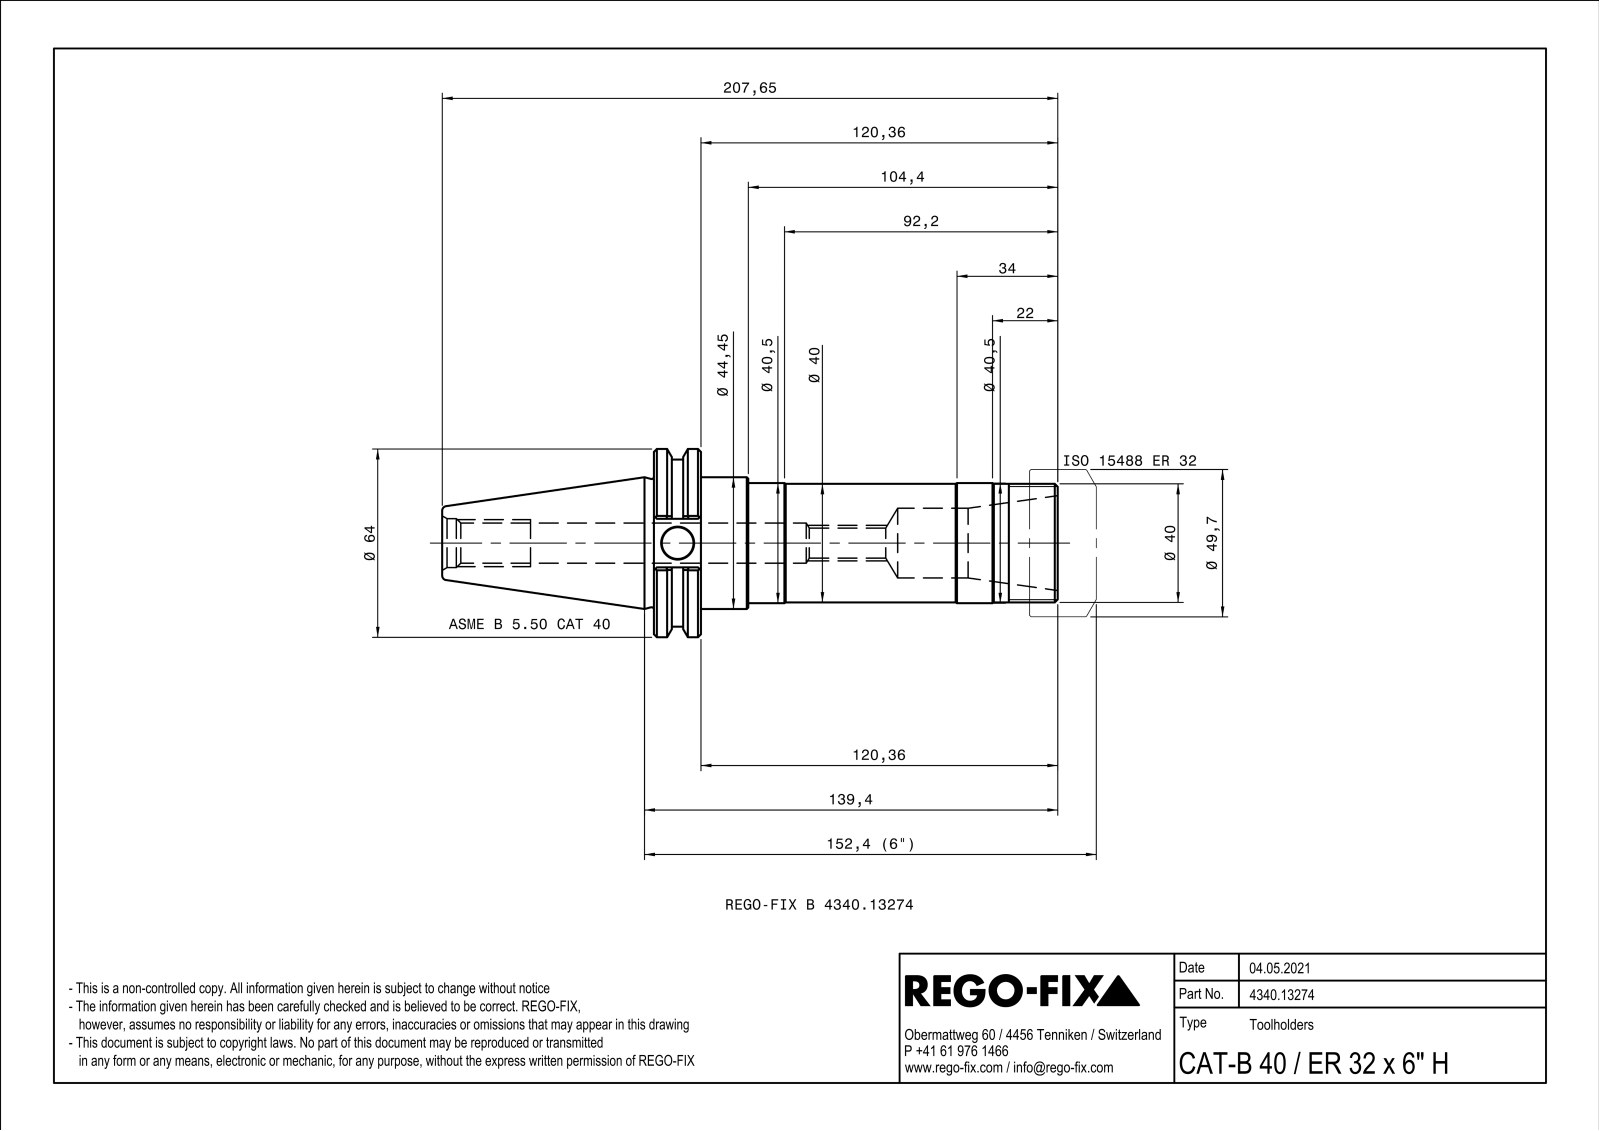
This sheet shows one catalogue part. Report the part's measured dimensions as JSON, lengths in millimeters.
{"part_name": "NOCUT", "step_written_by": "SIEMENS PLM Software Solid Edge ST10 (AUTOMOTIVE_DESIGN)", "units": "millimeters", "bodies": {"solids": 1, "faces": 123, "planar": 31, "cylindrical": 36, "other": 56}, "overall_size": [207.65, 63.5, 60.79], "volume_mm3": 212938, "surface_area_mm2": 43414, "round_holes": [[3.24, 2], [3.9, 2], [10.7, 1], [13.53, 1], [16.5, 1], [23.5, 1]], "round_bosses_or_shafts": [[63.5, 1], [56.36, 1], [44.45, 1], [40.5, 1], [40, 1]], "partial_cylinders_radius": [[0.5, 4]], "face_to_face_distances": [15.87, 120.36, 136.23, 47.33, 16.38, 207.65, 87.29, 71.42, 126.35, 5.99]}
